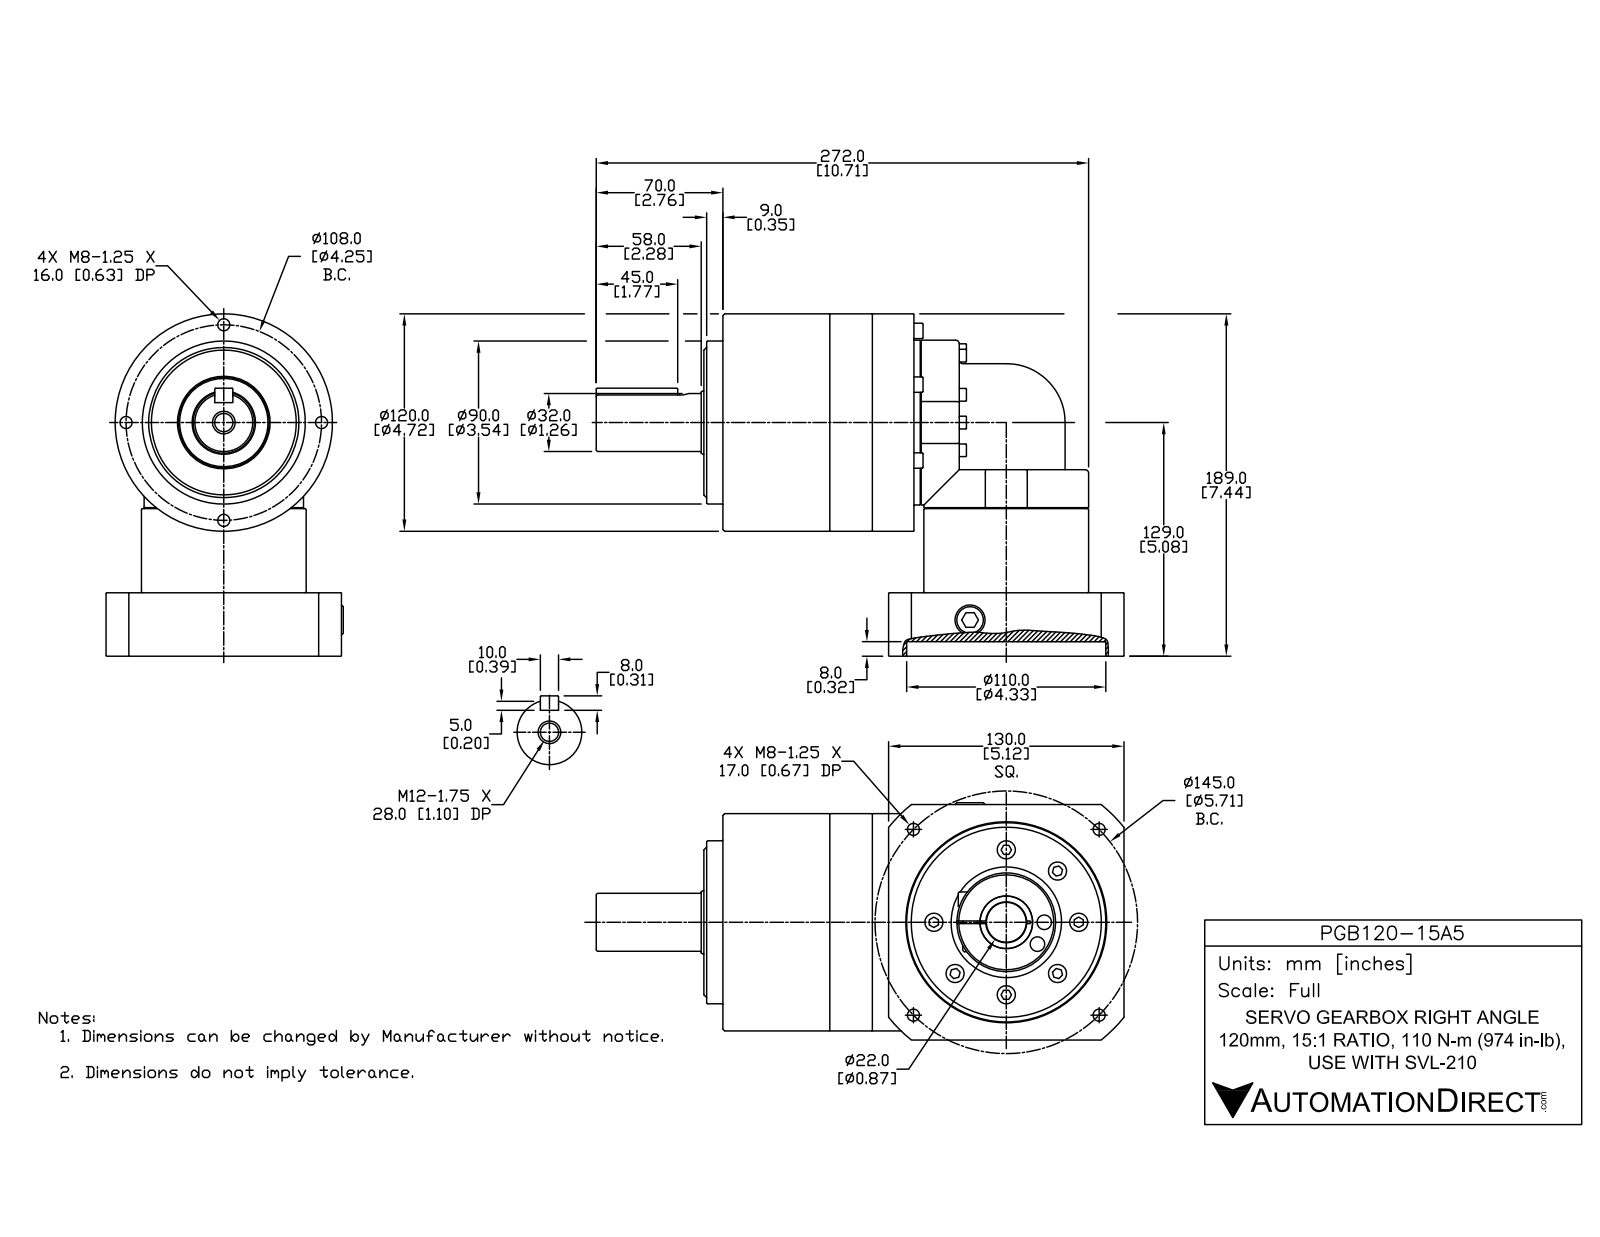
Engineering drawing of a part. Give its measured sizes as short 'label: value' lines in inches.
name: PGB120-15A5
written by: SolidWorks 2014 (AUTOMOTIVE_DESIGN)
unit: in
bodies: 2 solids, 652 faces (277 planar, 160 cylindrical, 215 other)
size: 11.476 × 7.441 × 5.157
volume: 145.3 in³; area: 298.2 in²
holes: 7× ⌀0.262, 6× ⌀0.217, 2× ⌀0.315, 1× ⌀0.262, 1× ⌀0.346, 1× ⌀0.398, 1× ⌀0.561, 1× ⌀0.866, 1× ⌀2.402, 1× ⌀4.134, 1× ⌀4.331
bosses: 9× ⌀0.276, 7× ⌀0.394, 6× ⌀0.335, 6× ⌀0.197, 2× ⌀3.583, 1× ⌀4.724, 1× ⌀3.543, 1× ⌀3.465
rounds: 6× R0.079, 2× R1.28, 1× R0.131, 1× R0.197, 1× R0.276, 1× R3.287
face distances: 0.02, 4.567, 5.118, 1.378, 4.291, 0.236, 1.142, 0.157, 0.689, 4.154
hole spacings: 0.836, 2.156, 2.379, 3.56, 4.199, 1.65, 2.126, 2.855
